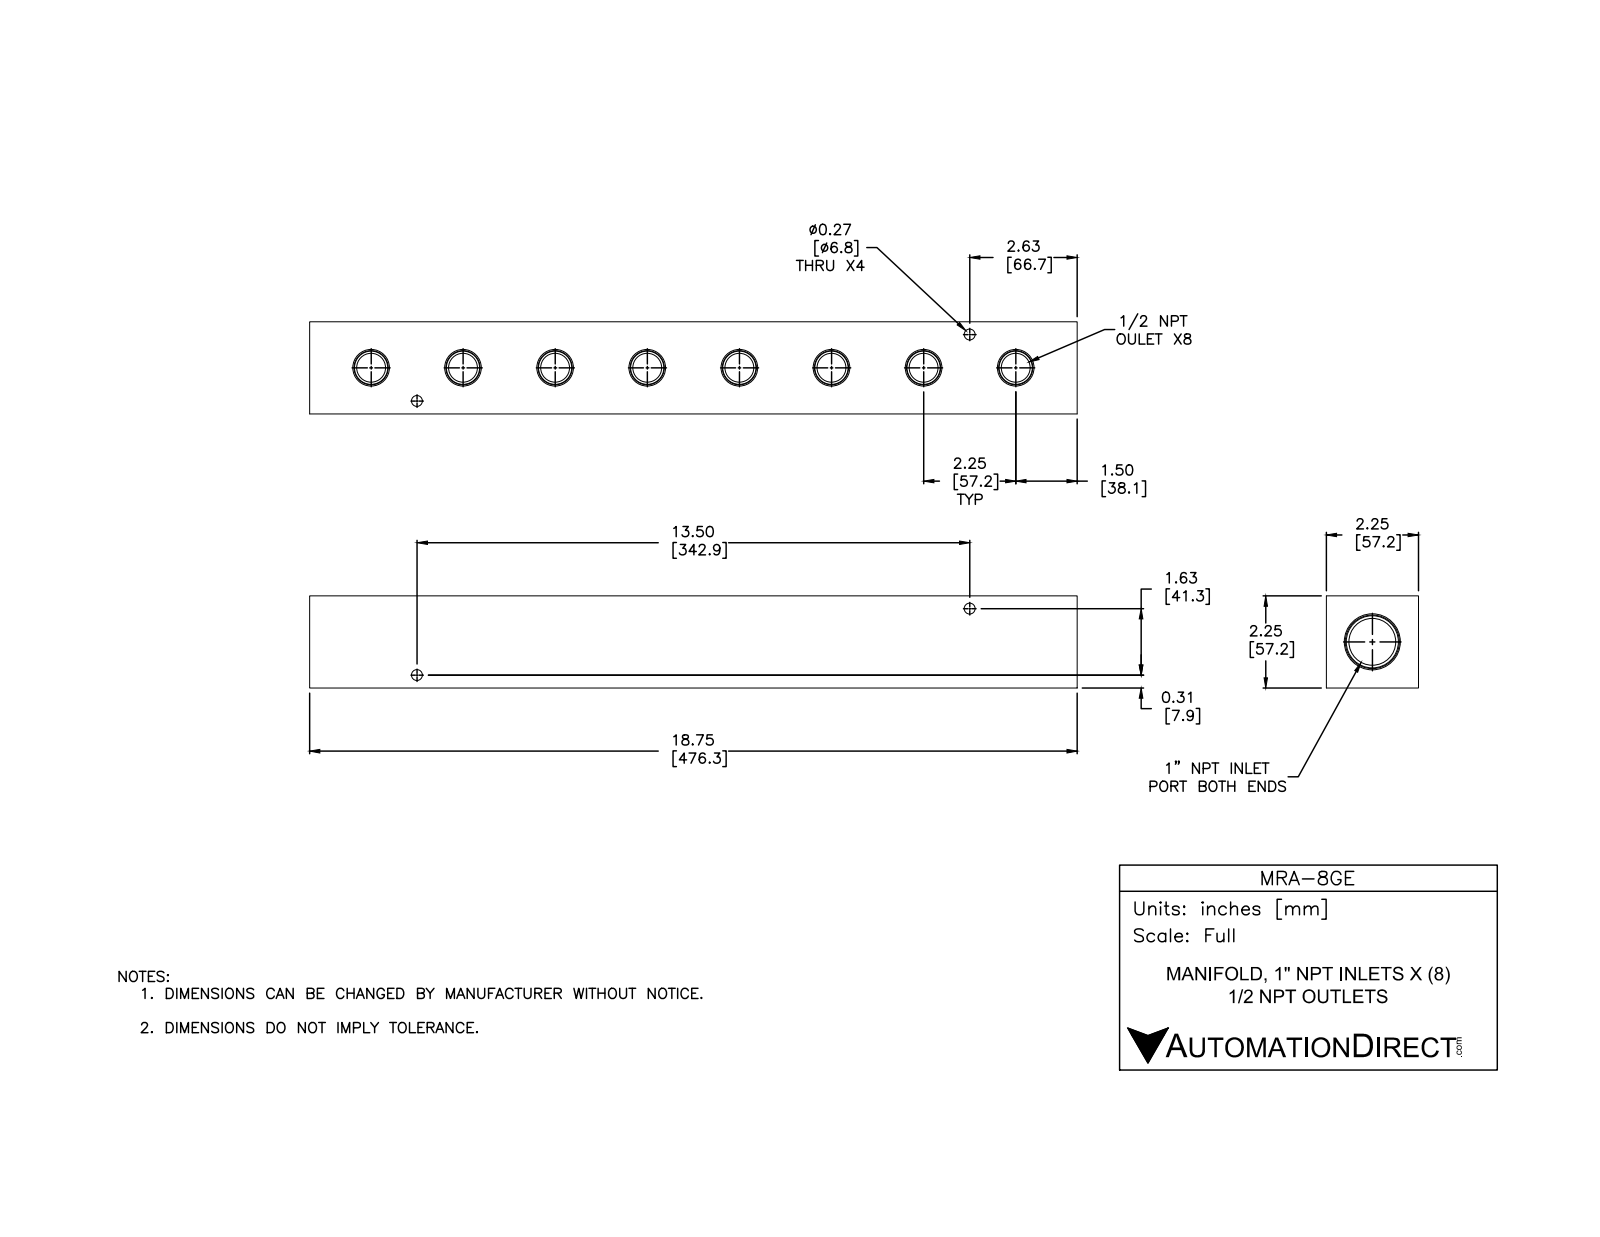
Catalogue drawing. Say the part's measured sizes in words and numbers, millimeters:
The part is named "MRA-8GE". Its 3-D file was written by "SolidWorks 2015 (CONFIG_CONTROL_DESIGN)". It is 1 solid with 90 faces: 16 planar, 34 cylindrical and 40 other. Overall it measures 476.3 by 57.2 by 57.2 millimeters. Its volume is 1 187 000 cubic millimeters and its surface area 165 400 square millimeters. Round holes: 8 of diameter 17.9, 4 of diameter 6.8, 1 of diameter 29. The main face-to-face distances are 57.2, 476.3, 43.7, 13.5, 16.8, 459.5, 442.7. The hole center spacings are 57.2, 114.3, 35.3, 171.5, 228.6, 285.8, 345.4, 372.1.
